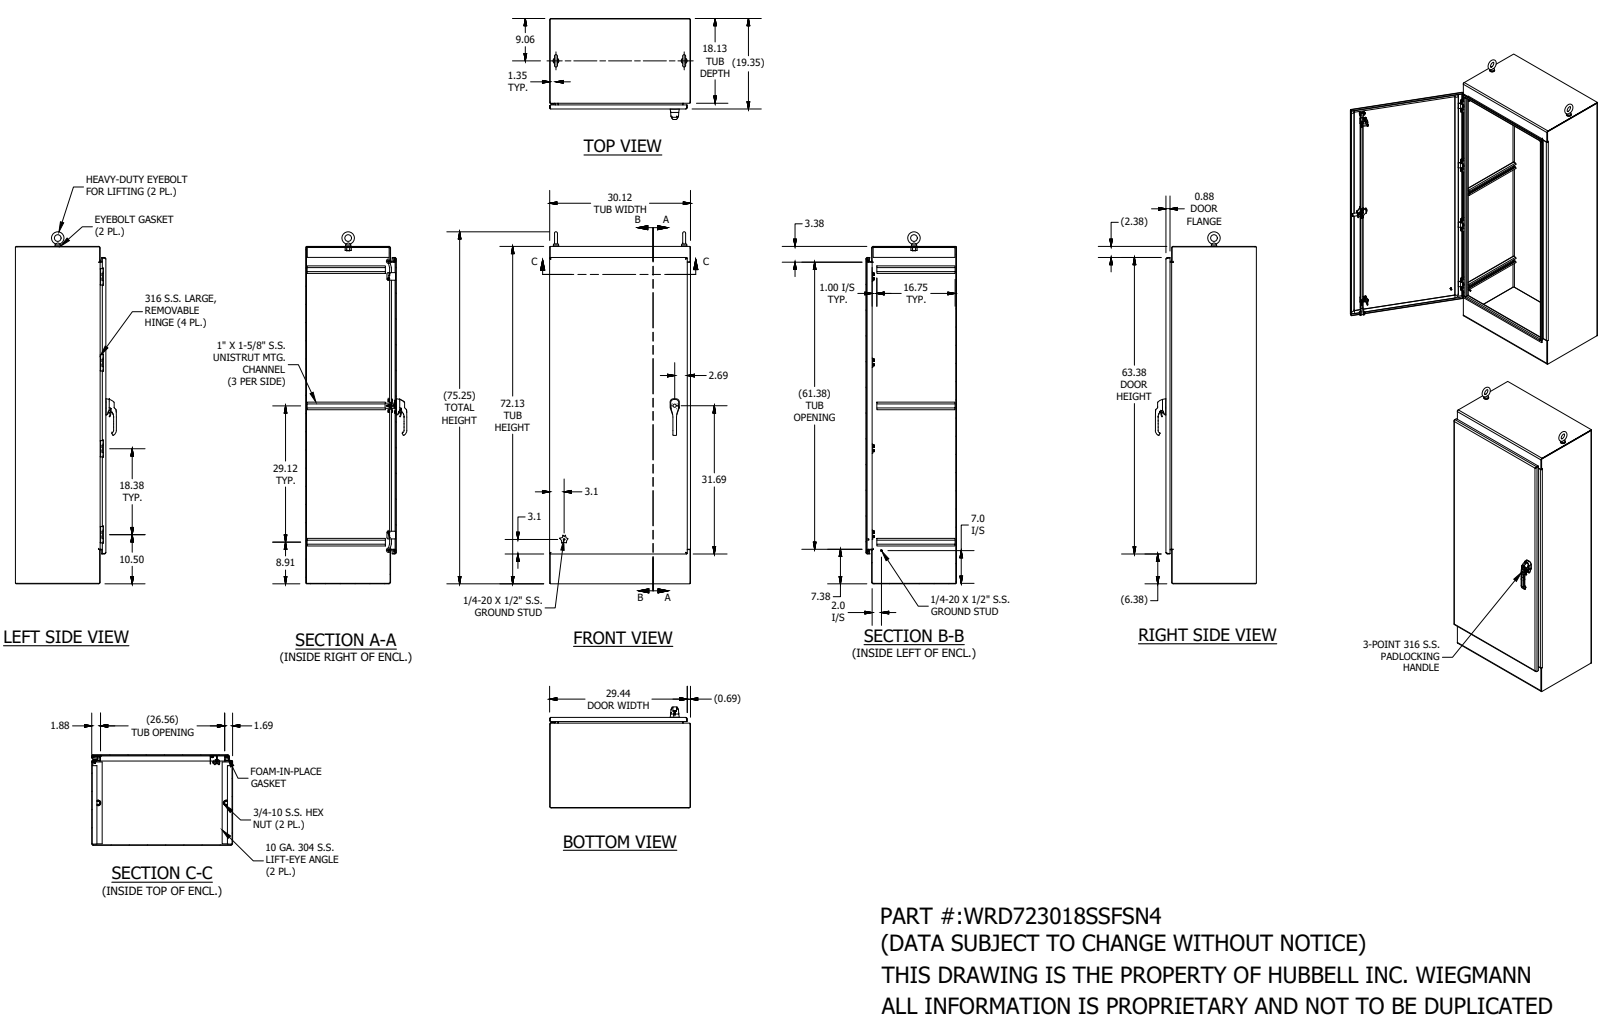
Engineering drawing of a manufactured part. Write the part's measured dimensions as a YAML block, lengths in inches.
part_name: "WRD723018SSFSN4"
step_written_by: "SolidWorks 2019 (AUTOMOTIVE_DESIGN)"
units: inches
bodies: {solids: 103, faces: 3881, planar: 1580, cylindrical: 1362, other: 939}
overall_size: [75.248, 30.129, 21.598]
volume: 1034
surface_area: 19236
round_holes:
  - {diameter: 0.14, count: 24}
  - {diameter: 0.195, count: 8}
  - {diameter: 0.262, count: 8}
  - {diameter: 0.266, count: 8}
  - {diameter: 0.294, count: 8}
  - {diameter: 0.65, count: 8}
  - {diameter: 0.136, count: 4}
  - {diameter: 0.164, count: 4}
  - {diameter: 0.187, count: 4}
  - {diameter: 0.201, count: 4}
  - {diameter: 0.213, count: 3}
  - {diameter: 0.281, count: 3}
round_bosses_or_shafts:
  - {diameter: 0.625, count: 8}
  - {diameter: 0.25, count: 7}
  - {diameter: 0.237, count: 4}
  - {diameter: 0.236, count: 3}
  - {diameter: 1.25, count: 2}
  - {diameter: 1.12, count: 2}
  - {diameter: 1, count: 2}
  - {diameter: 0.75, count: 2}
partial_cylinders:
  - {radius: 0.02, count: 172}
  - {radius: 0.012, count: 114}
  - {radius: 0.125, count: 34}
  - {radius: 0.019, count: 21}
  - {radius: 0.062, count: 18}
  - {radius: 0.05, count: 14}
  - {radius: 0.063, count: 14}
  - {radius: 0.079, count: 14}
face_to_face_distances: [0.104, 30.021, 19.245, 19.141, 19.349, 19.245, 0.104, 29.917, 30.125, 72.021]
hole_center_spacings: [0.018, 0.012, 0.023, 0.024, 0.38, 0.76, 1, 18.375]
